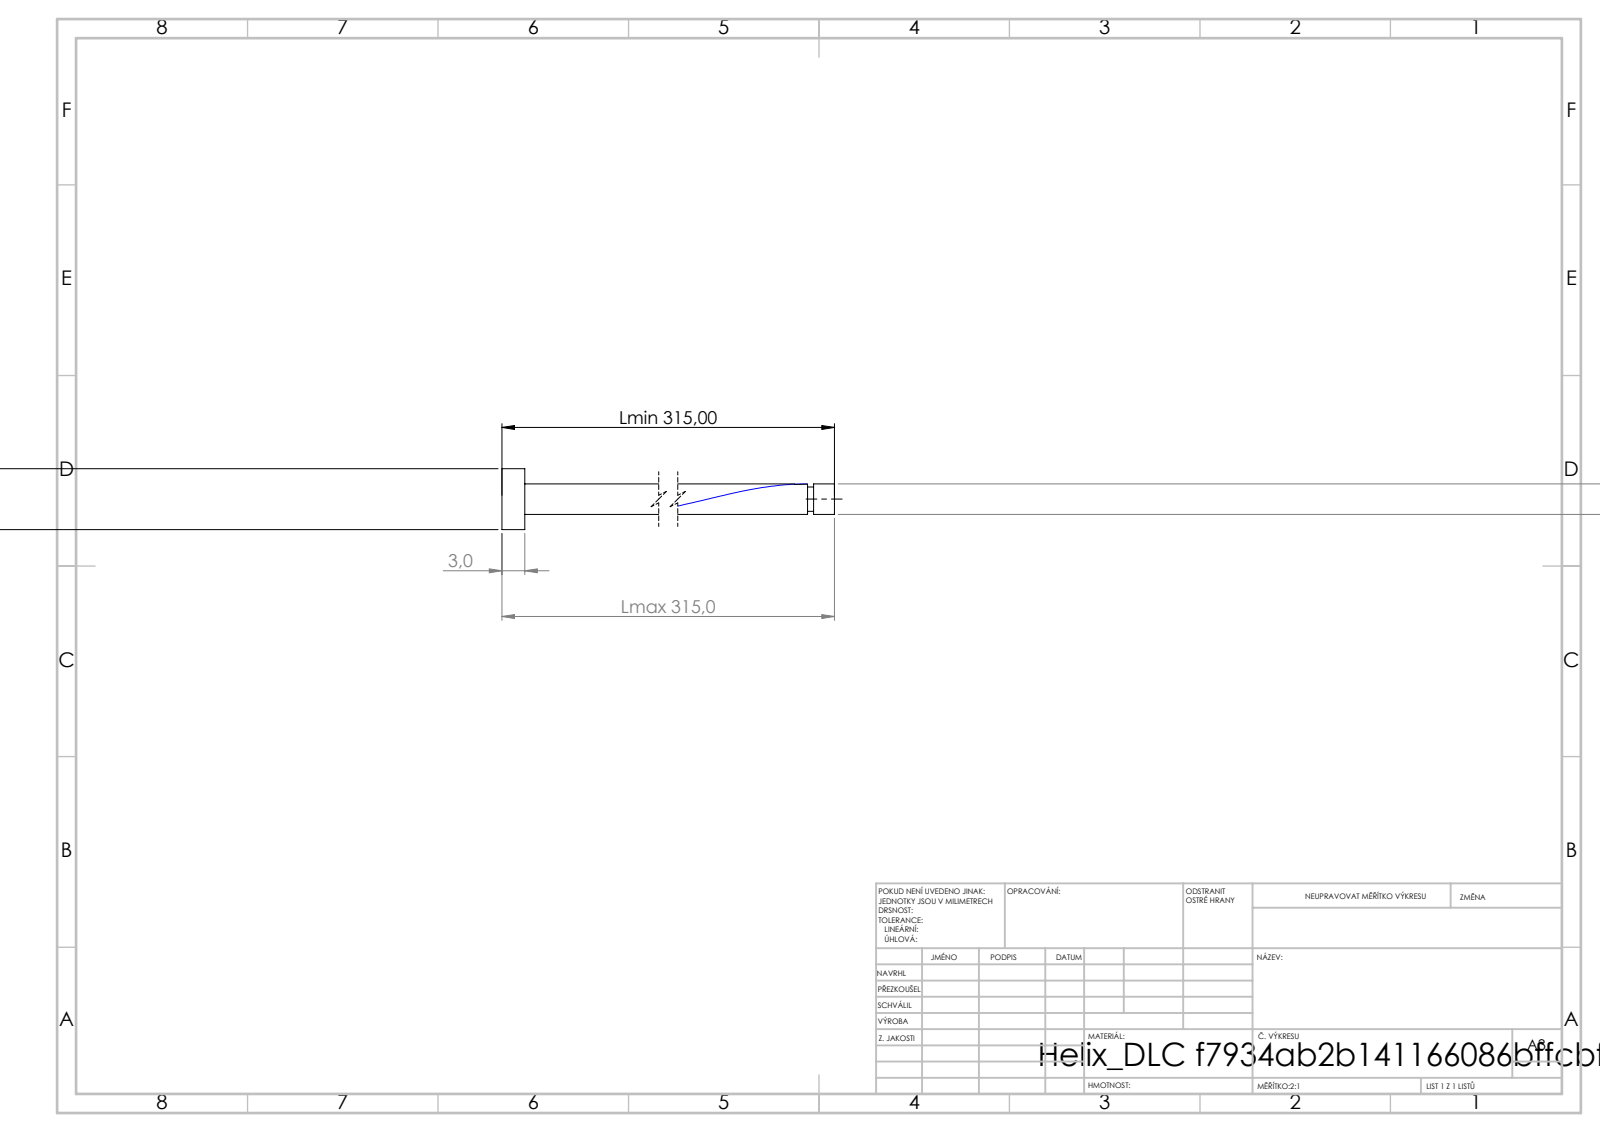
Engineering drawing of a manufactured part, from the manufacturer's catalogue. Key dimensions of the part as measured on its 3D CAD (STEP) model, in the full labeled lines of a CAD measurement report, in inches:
STEP written by: SolidWorks 2019 (CONFIG_CONTROL_DESIGN)
Units: inches
Bodies: 1 solid, 16 faces (6 planar, 9 cylindrical, 1 other)
Overall size (bounding box): 12.402 × 0.315 × 0.315
Volume: 0.3 in³ · Surface area: 8.502 in²
Round bosses / shafts (diameter × count): ⌀0.315 ×1, ⌀0.157 ×1, ⌀0.126 ×1
Main face-to-face distances: 0.118, 12.402, 12.283, 12.294, 12.176, 0.107, 12.263, 12.144, 0.031, 0.139
